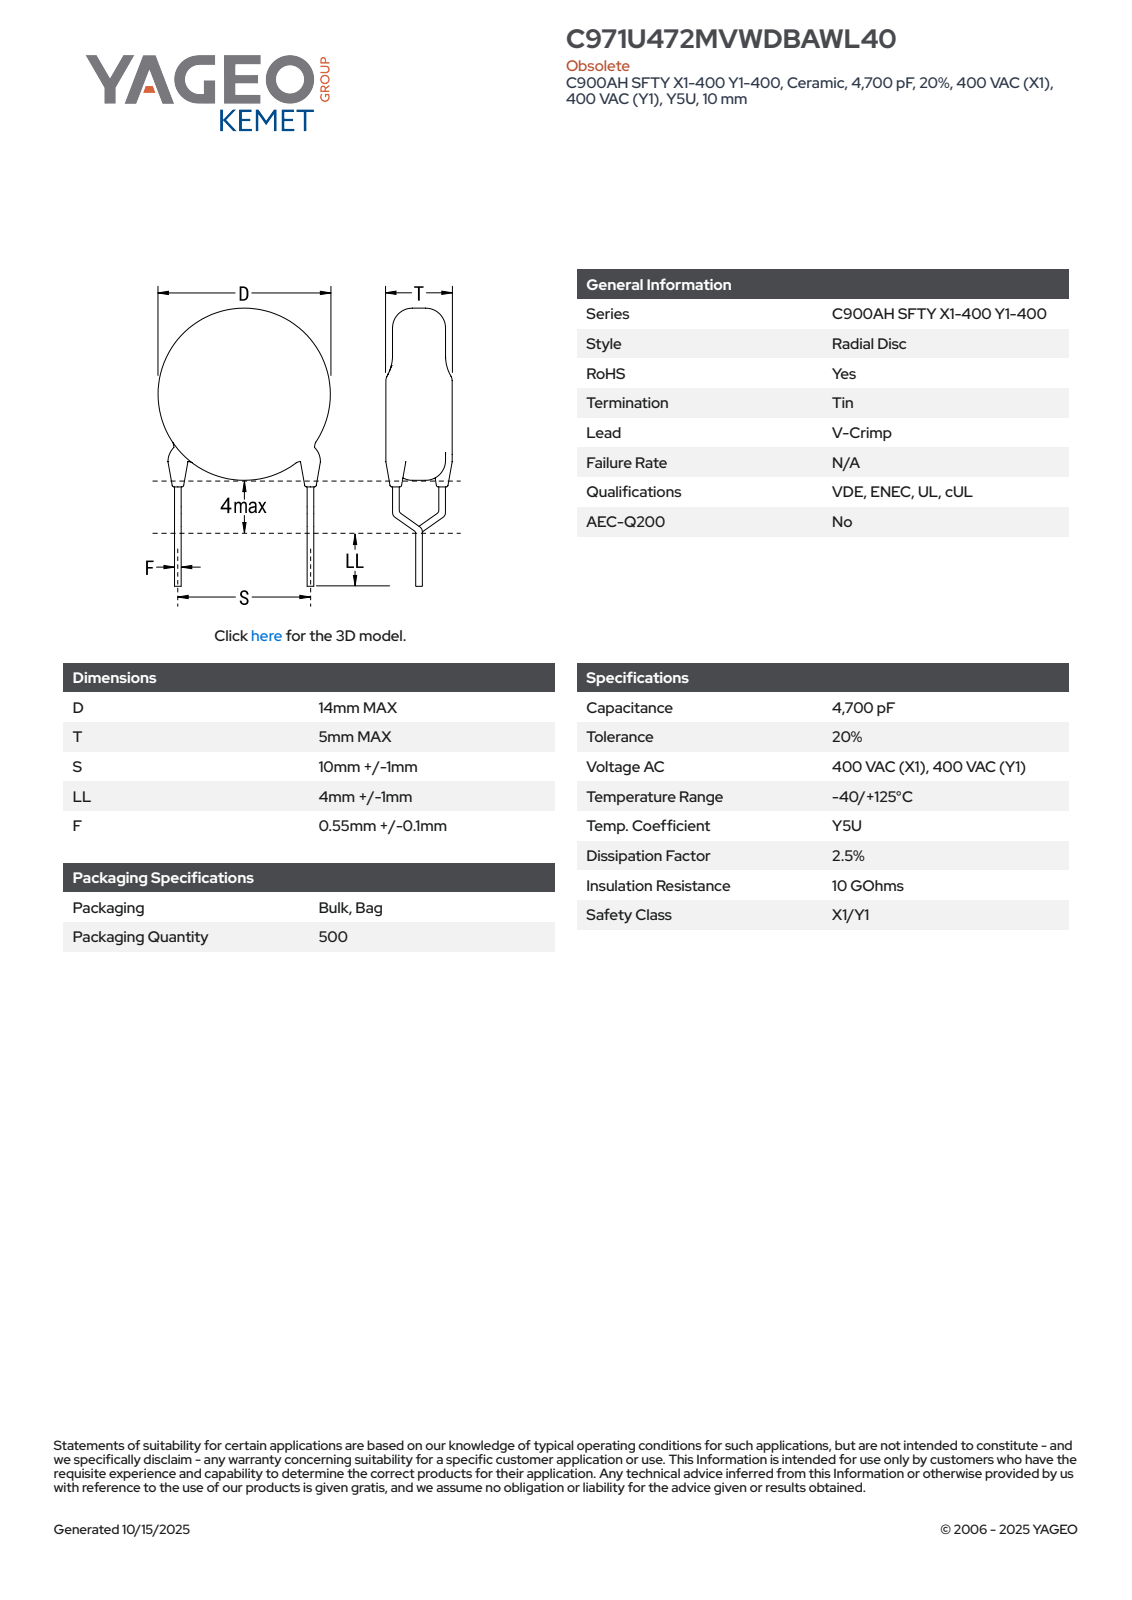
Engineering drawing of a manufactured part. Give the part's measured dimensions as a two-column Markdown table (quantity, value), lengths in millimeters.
| quantity | value |
| --- | --- |
| part name | CCD_VCC900_D14T5S10LL5F0.65 |
| STEP written by | SolidWorks 2014 (AUTOMOTIVE_DESIGN) |
| units | millimeters |
| bodies | 5 solids, 93 faces (65 planar, 16 cylindrical, 12 other) |
| overall size | 22.8 × 14 × 5 |
| volume | 761 mm³ |
| surface area | 557 mm² |
| round bosses / shafts (diameter × count) | 0.65 × 6, 14 × 1 |
| main face-to-face distances | 5, 7.9, 16.7, 8.8, 14.89, 6.99, 1.81, 0.49, 7.43, 0.35 |
